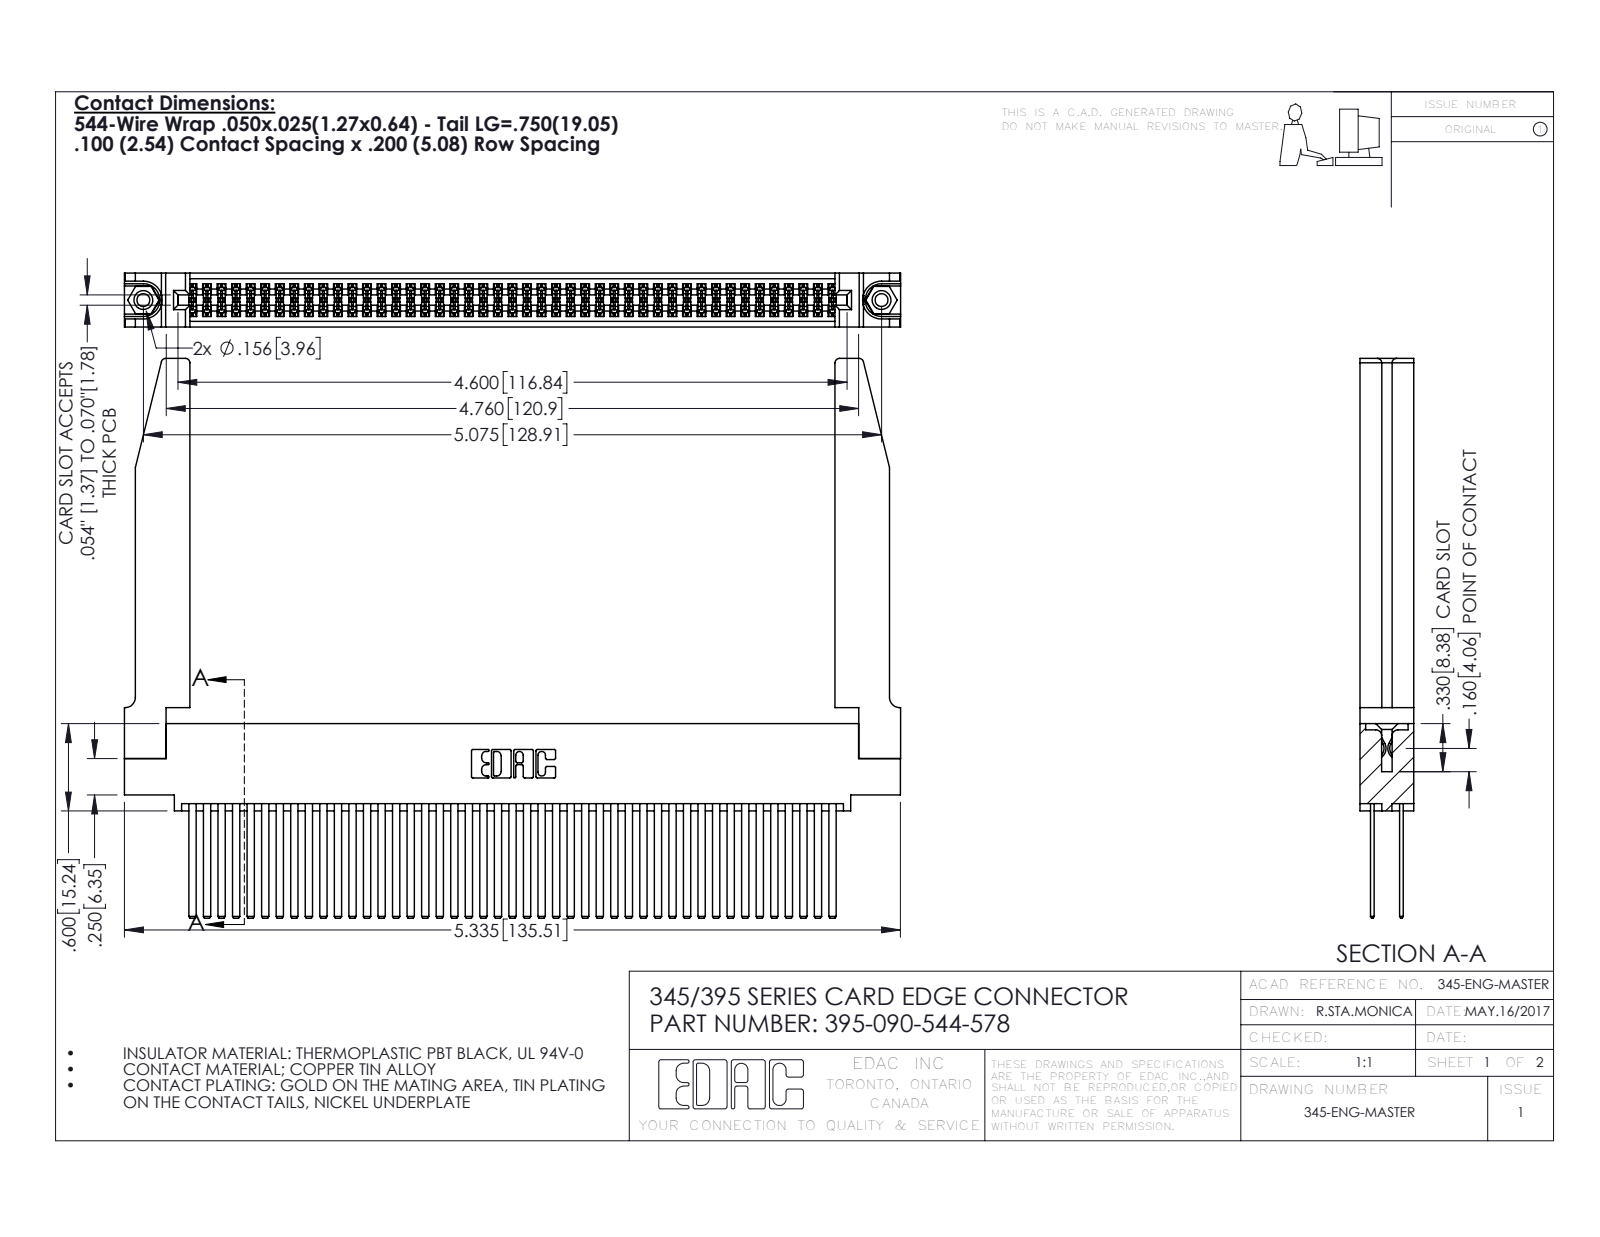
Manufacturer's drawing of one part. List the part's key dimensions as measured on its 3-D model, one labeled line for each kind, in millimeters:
Part name (STEP PRODUCT): 345 Part_0.110 Offset - 0.156 Dia-TH; 345-292-001_345-293-144; 395-090-544-578; 345-250-001_345-250-001-102 (+1 more)
STEP written by: SolidWorks 2016 (CONFIG_CONTROL_DESIGN)
Units: millimetres
Bodies: 95 solids, 4324 faces (2836 planar, 1436 cylindrical, 52 other)
Overall size (bounding box): 135.5 × 97.7 × 9.4
Volume: 22 160 mm³ · Surface area: 31 950 mm²
Round holes (diameter × count): ⌀2.3 ×2, ⌀3.2 ×2, ⌀4 ×2, ⌀1.6 ×1
Round bosses / shafts (diameter × count): ⌀3.9 ×2
Partial cylindrical surfaces — rounded edges, fillets, slot ends (radius × count): R0.2 ×135, R0.3 ×22, R0.8 ×8, R0.2 ×6, R0.8 ×6, R0.7 ×3, R0.4 ×2, R0.5 ×2
Main face-to-face distances: 1.8, 7.6, 2.5, 6.9, 0.6, 5.1, 9.4, 5.7, 4.4, 3.8
Hole centre spacings: 6.9, 122.9, 128.9
